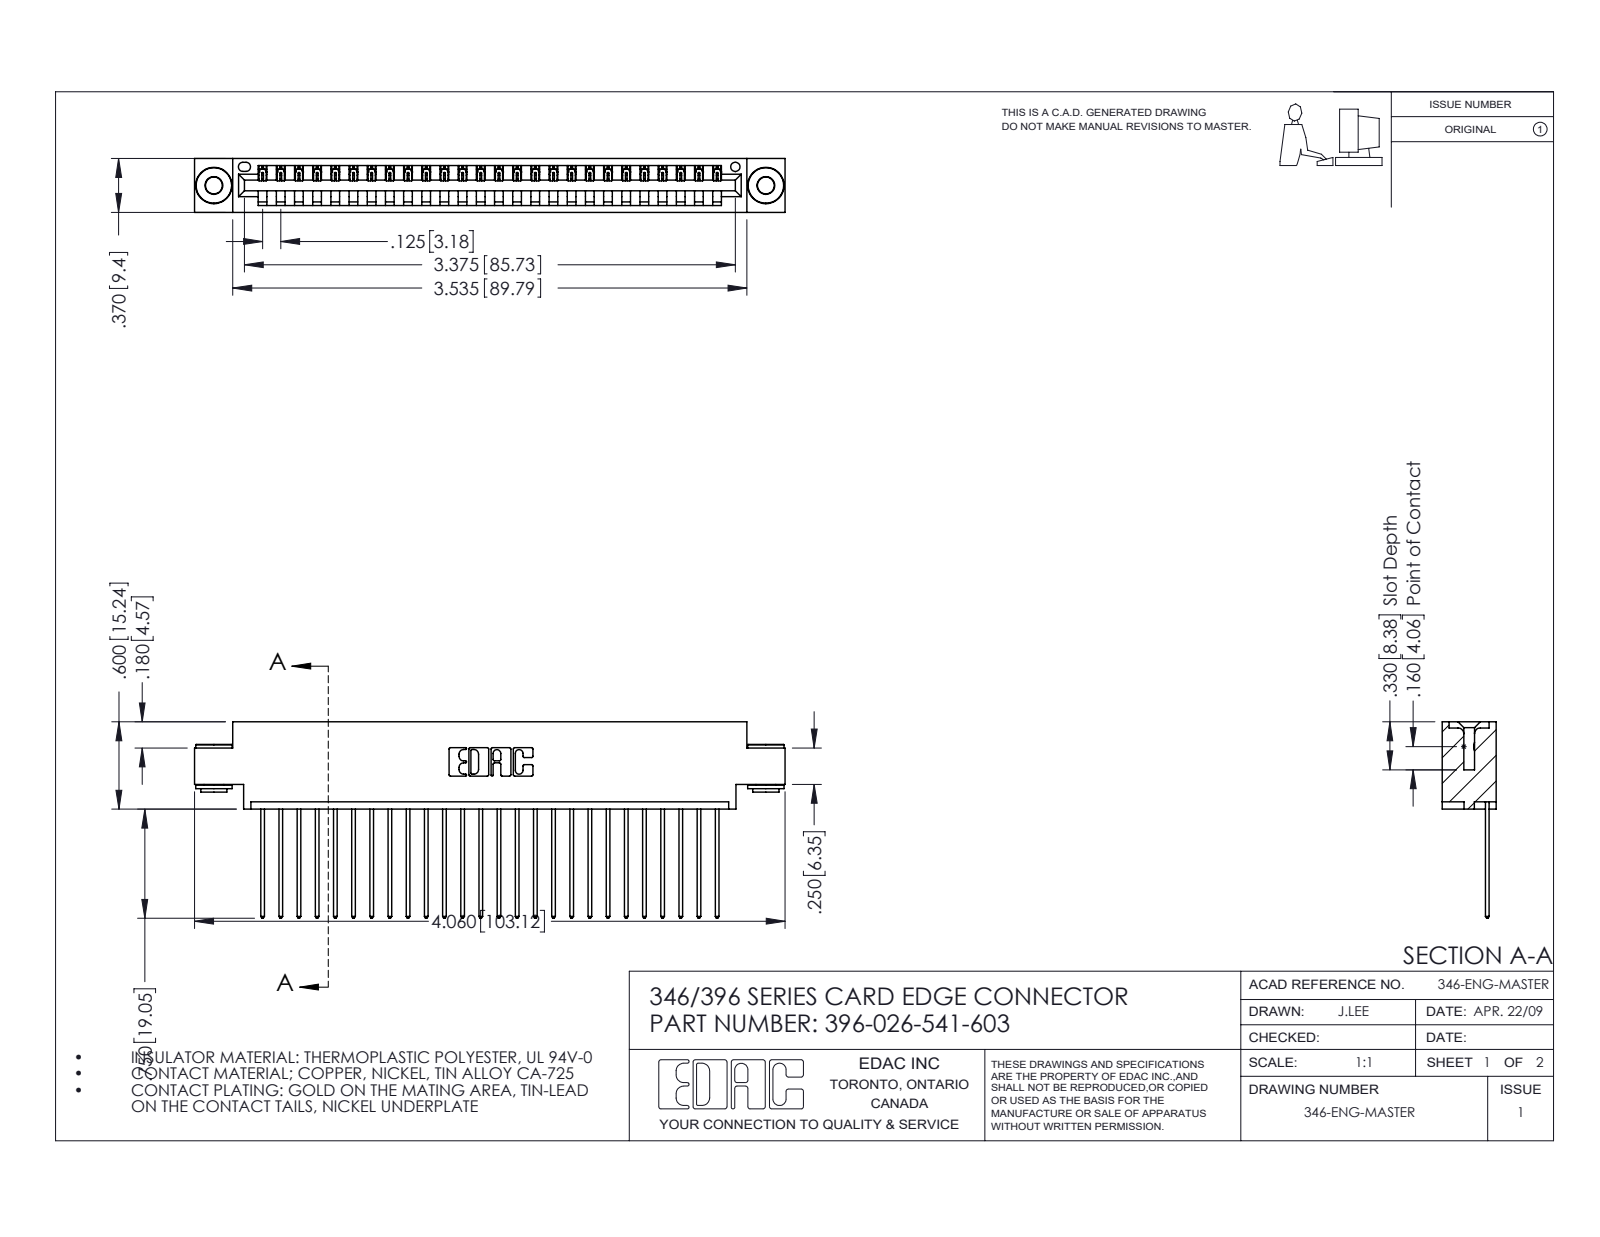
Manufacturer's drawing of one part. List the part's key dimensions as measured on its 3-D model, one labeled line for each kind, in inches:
Part name (STEP PRODUCT): 345-292-001_345-293-141; 345-250-002_345-250-002-102; 346 Part_0.170 Offset - 0.156 Dia-TH; 396-026-541-603
STEP written by: SolidWorks 2016 (CONFIG_CONTROL_DESIGN)
Units: inches
Bodies: 29 solids, 1672 faces (1130 planar, 534 cylindrical, 8 other)
Overall size (bounding box): 4.06 × 1.35 × 0.37
Volume: 0.593 in³ · Surface area: 19.93 in²
Round holes (diameter × count): ⌀0.116 ×2, ⌀0.156 ×2, ⌀0.064 ×1
Round bosses / shafts (diameter × count): ⌀0.25 ×2, ⌀0.18 ×2, ⌀0.136 ×2
Partial cylindrical surfaces — rounded edges, fillets, slot ends (radius × count): R0.006 ×52, R0.01 ×52, R0.01 ×22, R0.007 ×6, R0.031 ×6, R0.026 ×3, R0.031 ×2, R0.04 ×2
Main face-to-face distances: 0.048, 0.322, 0.37, 0.25, 0.025, 0.072, 0.298, 0.148, 0.222, 0.1
Hole centre spacings: 0.246, 3.587, 3.795
